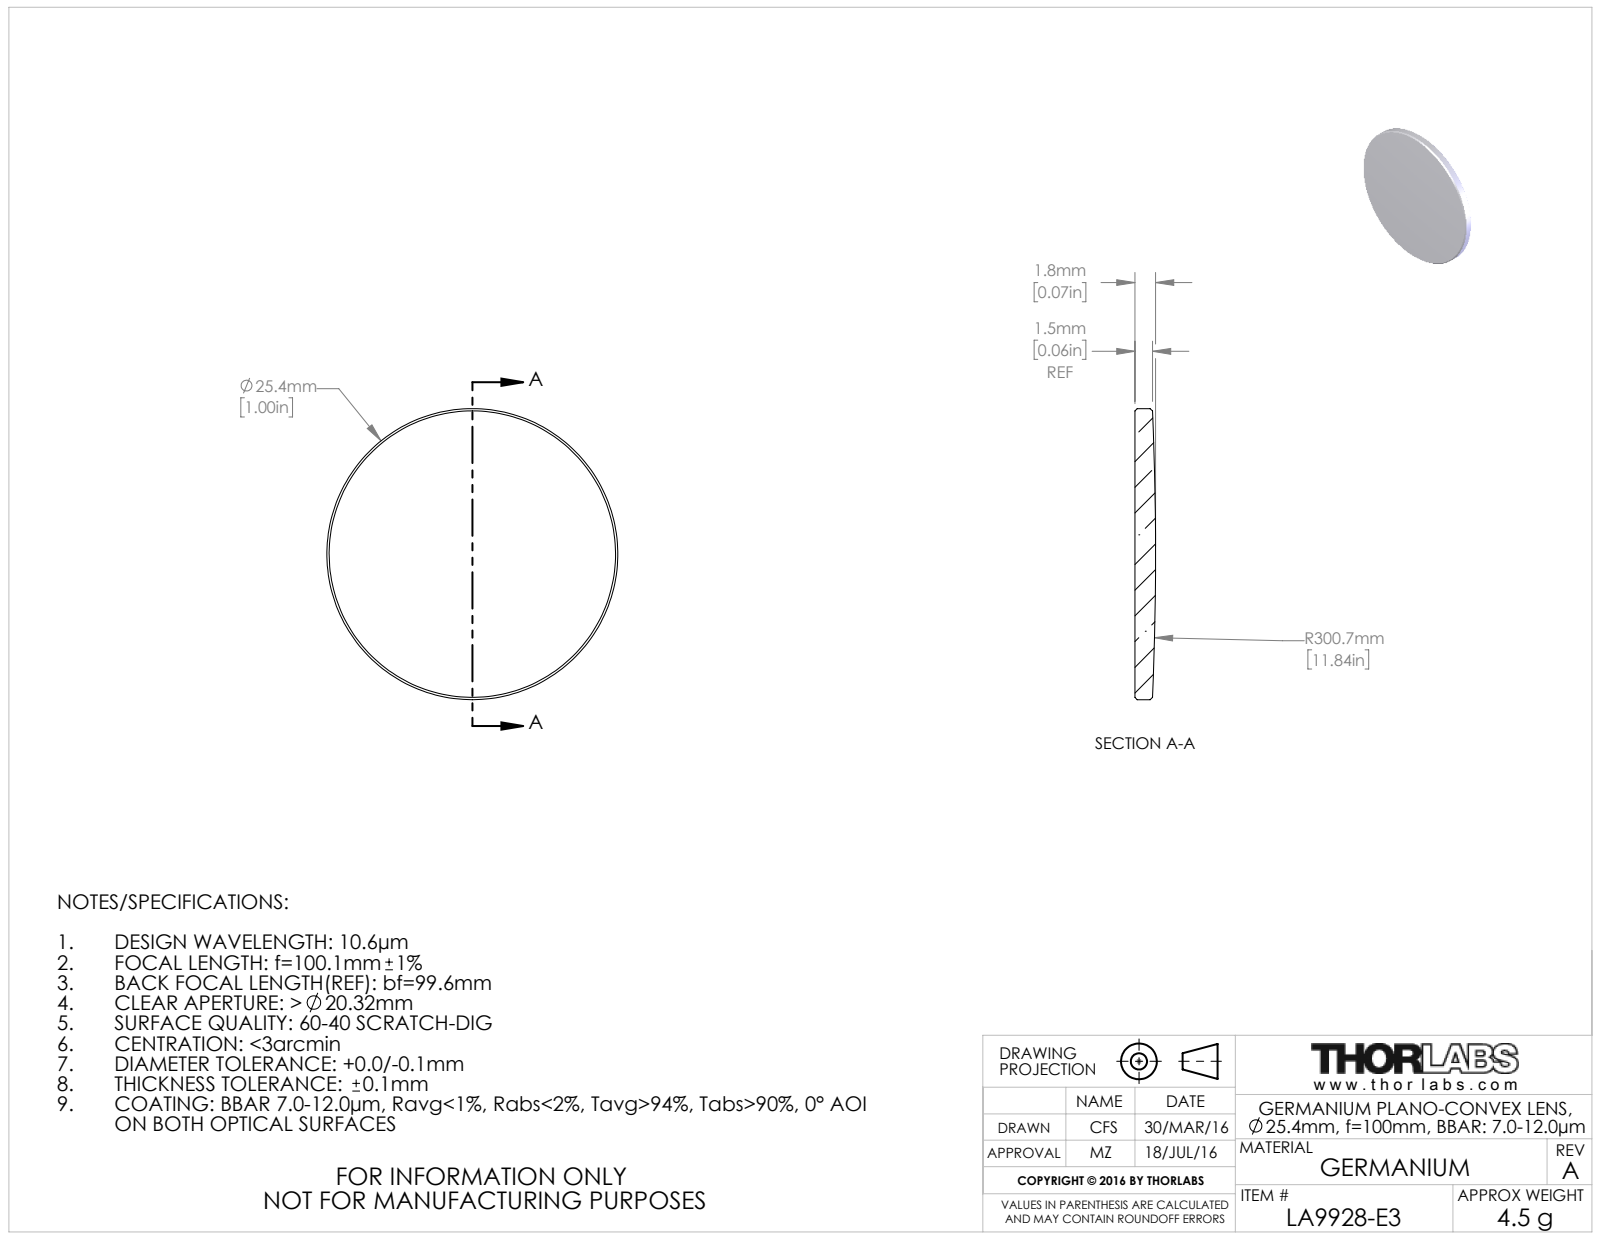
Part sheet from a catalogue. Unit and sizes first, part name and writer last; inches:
Units: inches
Overall size (bounding box): 1 × 1 × 0.071
Round bosses / shafts (diameter × count): ⌀1 ×1
Volume: 0.051 in³ · Surface area: 1.732 in²
Bodies: 1 solid, 9 faces (1 planar, 2 cylindrical, 6 other)
Part name (STEP PRODUCT): TTN049384-E0W
STEP written by: SolidWorks 2016 (CONFIG_CONTROL_DESIGN)
